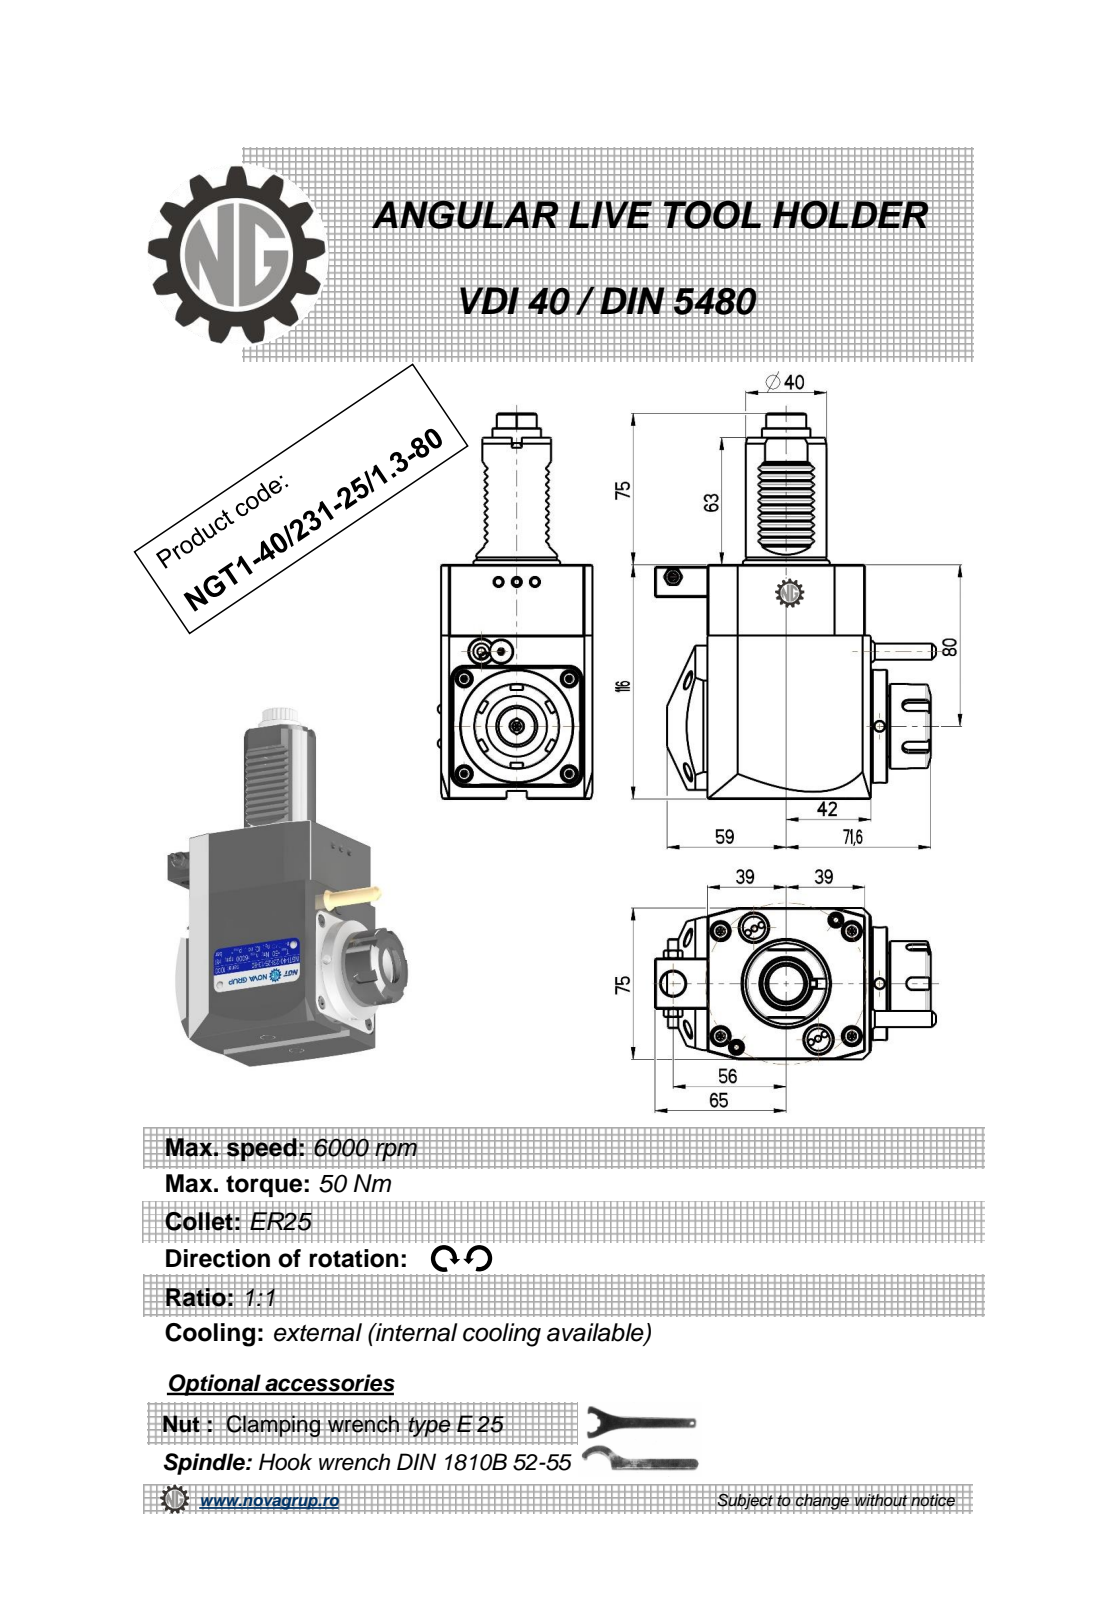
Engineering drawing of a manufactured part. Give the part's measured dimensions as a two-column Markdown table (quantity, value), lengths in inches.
| quantity | value |
| --- | --- |
| part name | NGT1_40_231_25_1_3_80 |
| STEP written by | PRO/ENGINEER BY PARAMETRIC TECHNOLOGY CORPORATION, 2010280 (CONFIG_CONTROL_DESIGN) |
| units | inches |
| bodies | 1 solid, 595 faces (229 planar, 191 cylindrical, 175 other) |
| overall size | 7.52 × 5.478 × 2.953 |
| volume | 52.79 in³ |
| surface area | 109.7 in² |
| round holes (diameter × count) | 0.197 × 3, 0.118 × 1, 0.165 × 1, 0.374 × 1, 0.472 × 1, 0.799 × 1 |
| round bosses / shafts (diameter × count) | 2.205 × 1, 1.693 × 1, 1.654 × 1, 1.575 × 1, 1.299 × 1, 0.945 × 1, 0.441 × 1, 0.353 × 1 |
| partial cylindrical surfaces (radius × count) | 0.082 × 48, 0.012 × 20, 0.01 × 12, 0.009 × 6, 0.118 × 5, 0.357 × 1, 0.391 × 1, 0.591 × 1 |
| main face-to-face distances | 2.953, 4.567, 3.189, 3.071, 0.118, 0.433, 0.315, 0.295, 3.181, 0.11 |
| hole center spacings | 1.523, 1.611, 2.815, 4.026, 4.969 |
